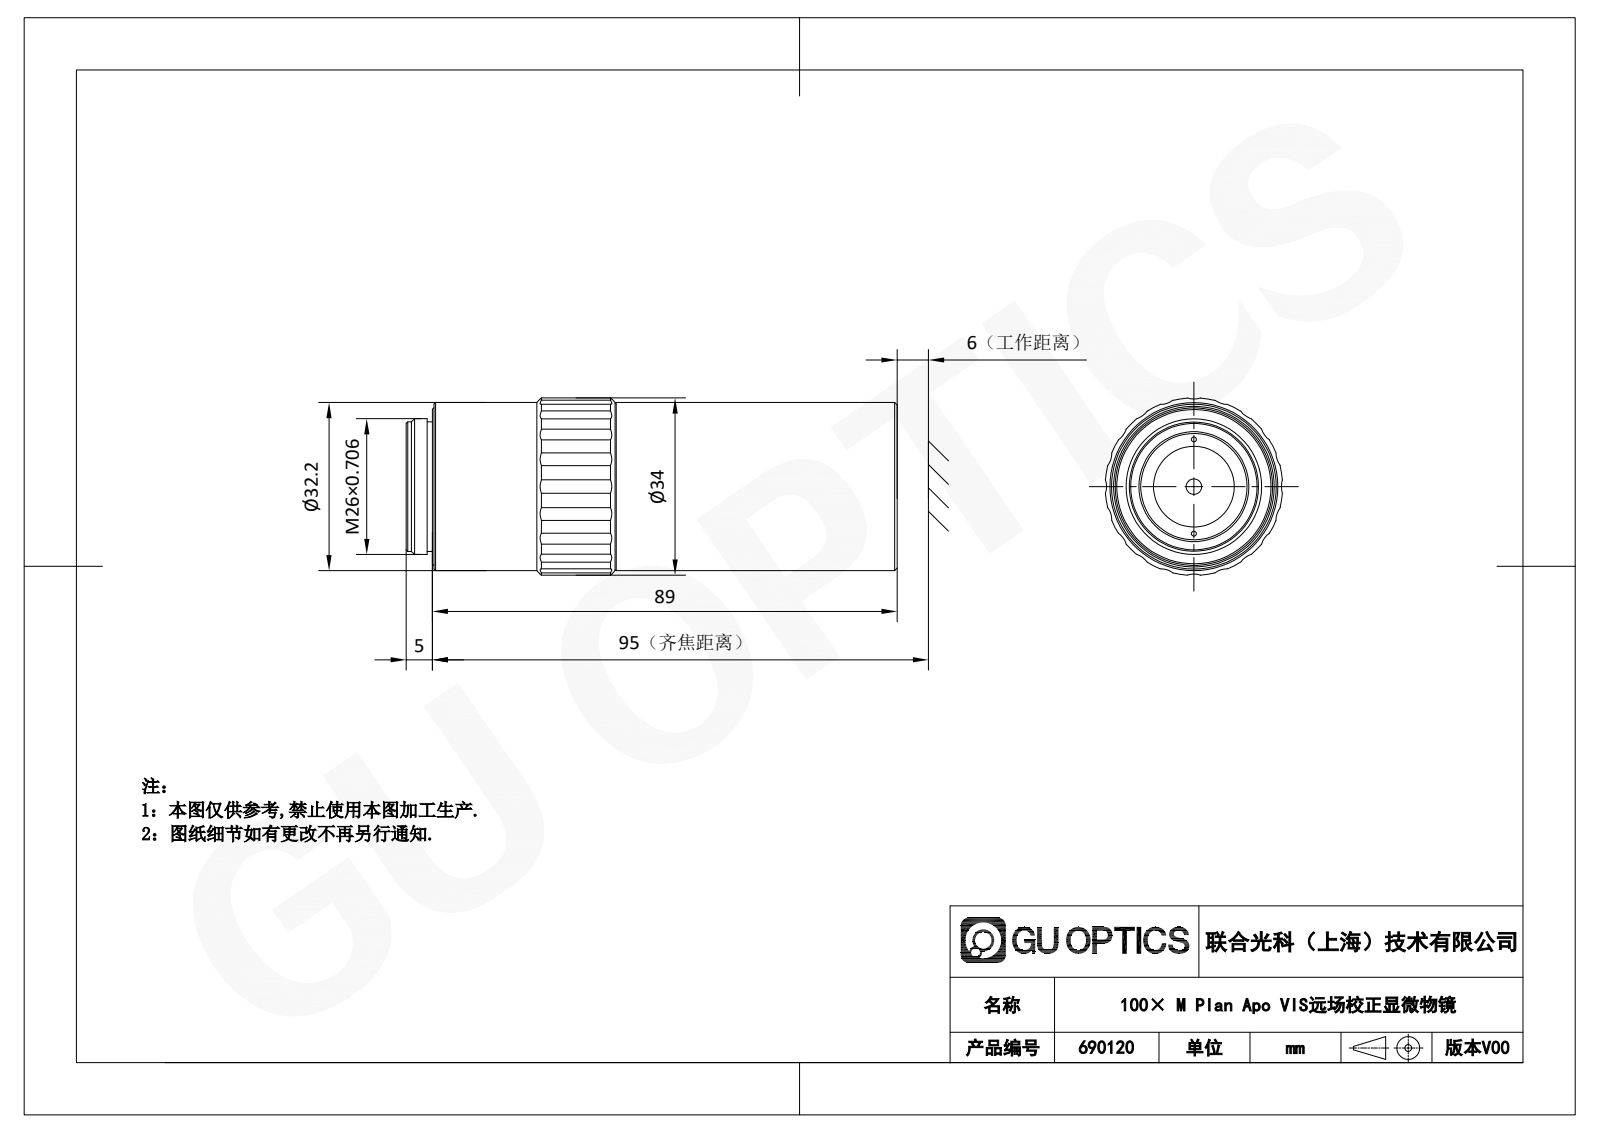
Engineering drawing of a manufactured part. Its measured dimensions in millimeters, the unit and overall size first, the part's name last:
Units: millimetres
Overall size (bounding box): 94 × 33.9 × 33.9
Round holes (diameter × count): ⌀2.01 ×10, ⌀1 ×2, ⌀2.01 ×2, ⌀3 ×1, ⌀15.5 ×1, ⌀20 ×1, ⌀20.5 ×1, ⌀21.4 ×1, ⌀23.8 ×1, ⌀26.8 ×1, ⌀27 ×1, ⌀27.9 ×1
Round bosses / shafts (diameter × count): ⌀32.2 ×1, ⌀31 ×1, ⌀30.2 ×1, ⌀29.9 ×1, ⌀27.5 ×1, ⌀26 ×1, ⌀24.8 ×1, ⌀21 ×1
Partial cylindrical surfaces — rounded edges, fillets, slot ends (radius × count): R4 ×20, R17 ×1
Main face-to-face distances: 1.5, 0.7, 5, 1, 3.5, 89, 94, 93.3, 6.5, 88
Hole centre spacings: 16.2, 9, 18
Volume: 25 330 mm³ · Surface area: 38 259 mm²
Bodies: 5 solids, 147 faces (26 planar, 88 cylindrical, 33 other)
Part name (STEP PRODUCT): X2_59165957_X0; X2_88C599705708_X0; X2_538B5708_X0; 690120 (+2 more)
STEP written by: SolidWorks 2020 (CONFIG_CONTROL_DESIGN)
